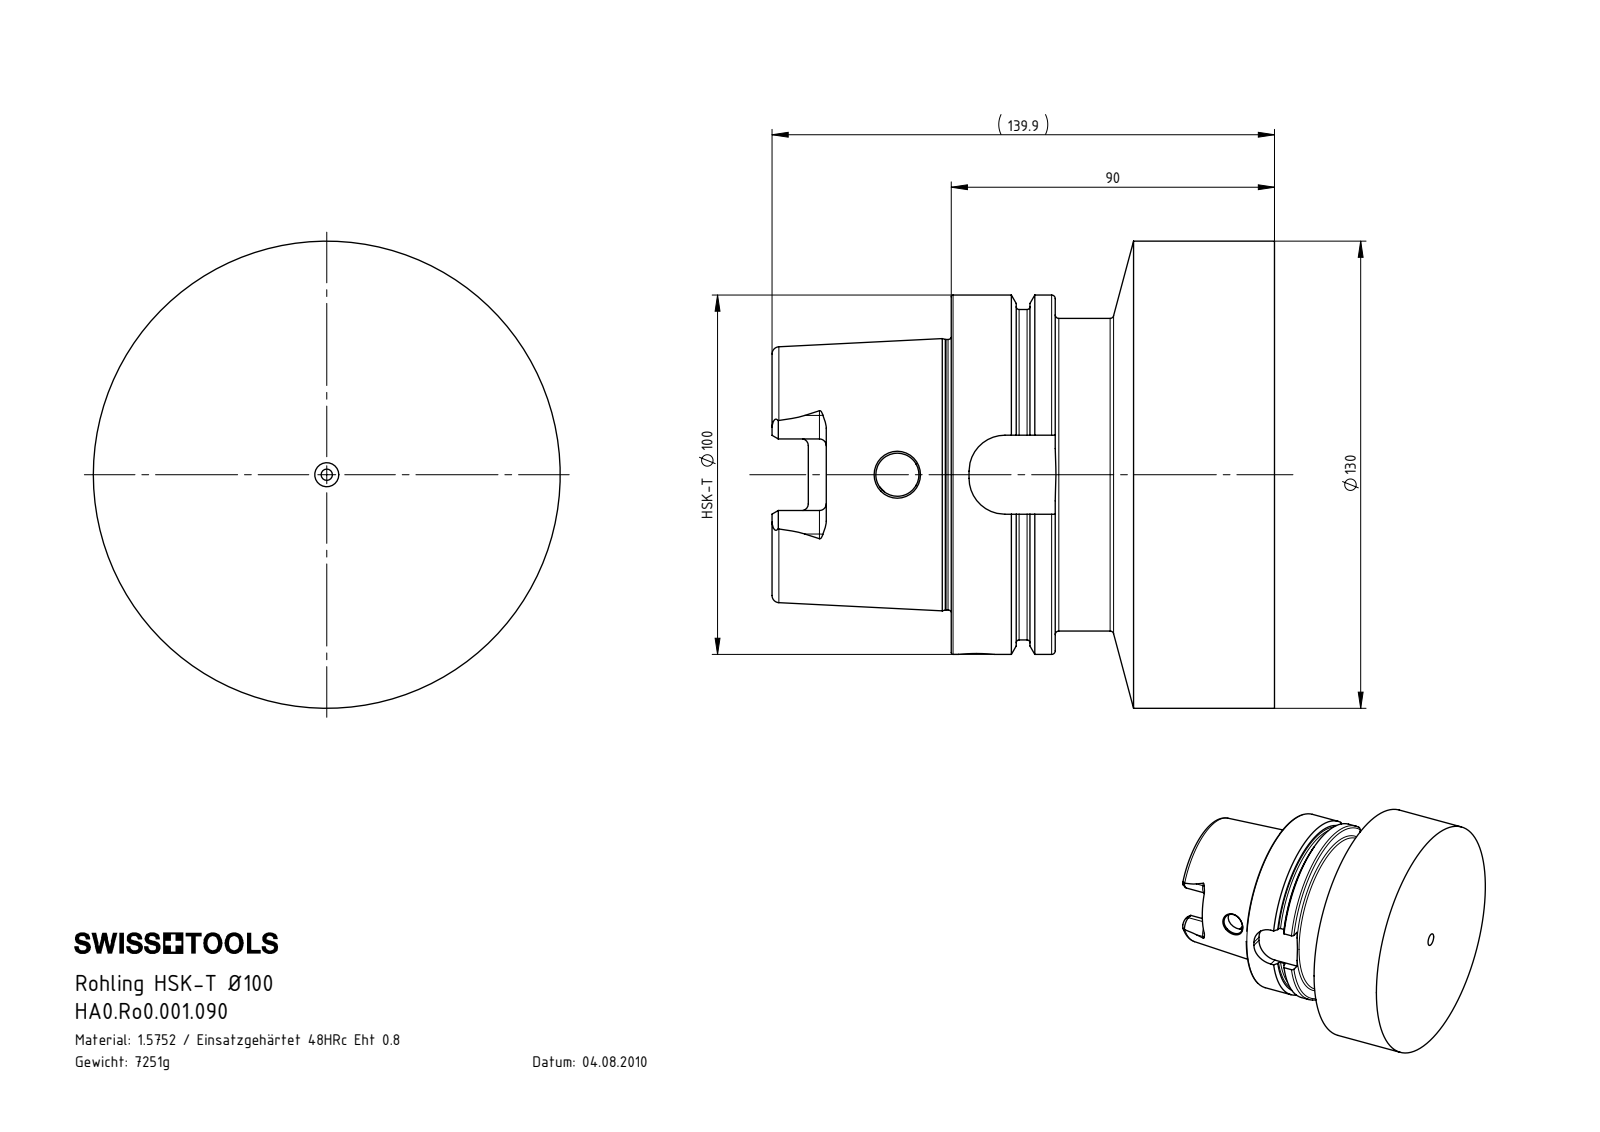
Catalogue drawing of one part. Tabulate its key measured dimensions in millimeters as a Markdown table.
| quantity | value |
| --- | --- |
| part name | HA0.Ro0.001.090 |
| STEP written by | SolidWorks 2017 (AUTOMOTIVE_DESIGN) |
| units | millimeters |
| bodies | 1 solid, 117 faces (38 planar, 33 cylindrical, 46 other) |
| overall size | 139.9 × 130 × 130 |
| volume | 923 615 mm³ |
| surface area | 84 836 mm² |
| round holes (diameter × count) | 3.15 × 1, 10 × 1, 12 × 1, 22.5 × 1, 26 × 1, 53 × 1, 63 × 1 |
| round bosses / shafts (diameter × count) | 130 × 1, 100 × 1, 91.95 × 1, 87 × 1, 75.26 × 1 |
| partial cylindrical surfaces (radius × count) | 1.9 × 6, 4.88 × 4, 10 × 4 |
| main face-to-face distances | 90, 12.45, 77.55, 28.95, 16.5, 61.05, 49.9, 62.35, 78.85, 139.9 |
